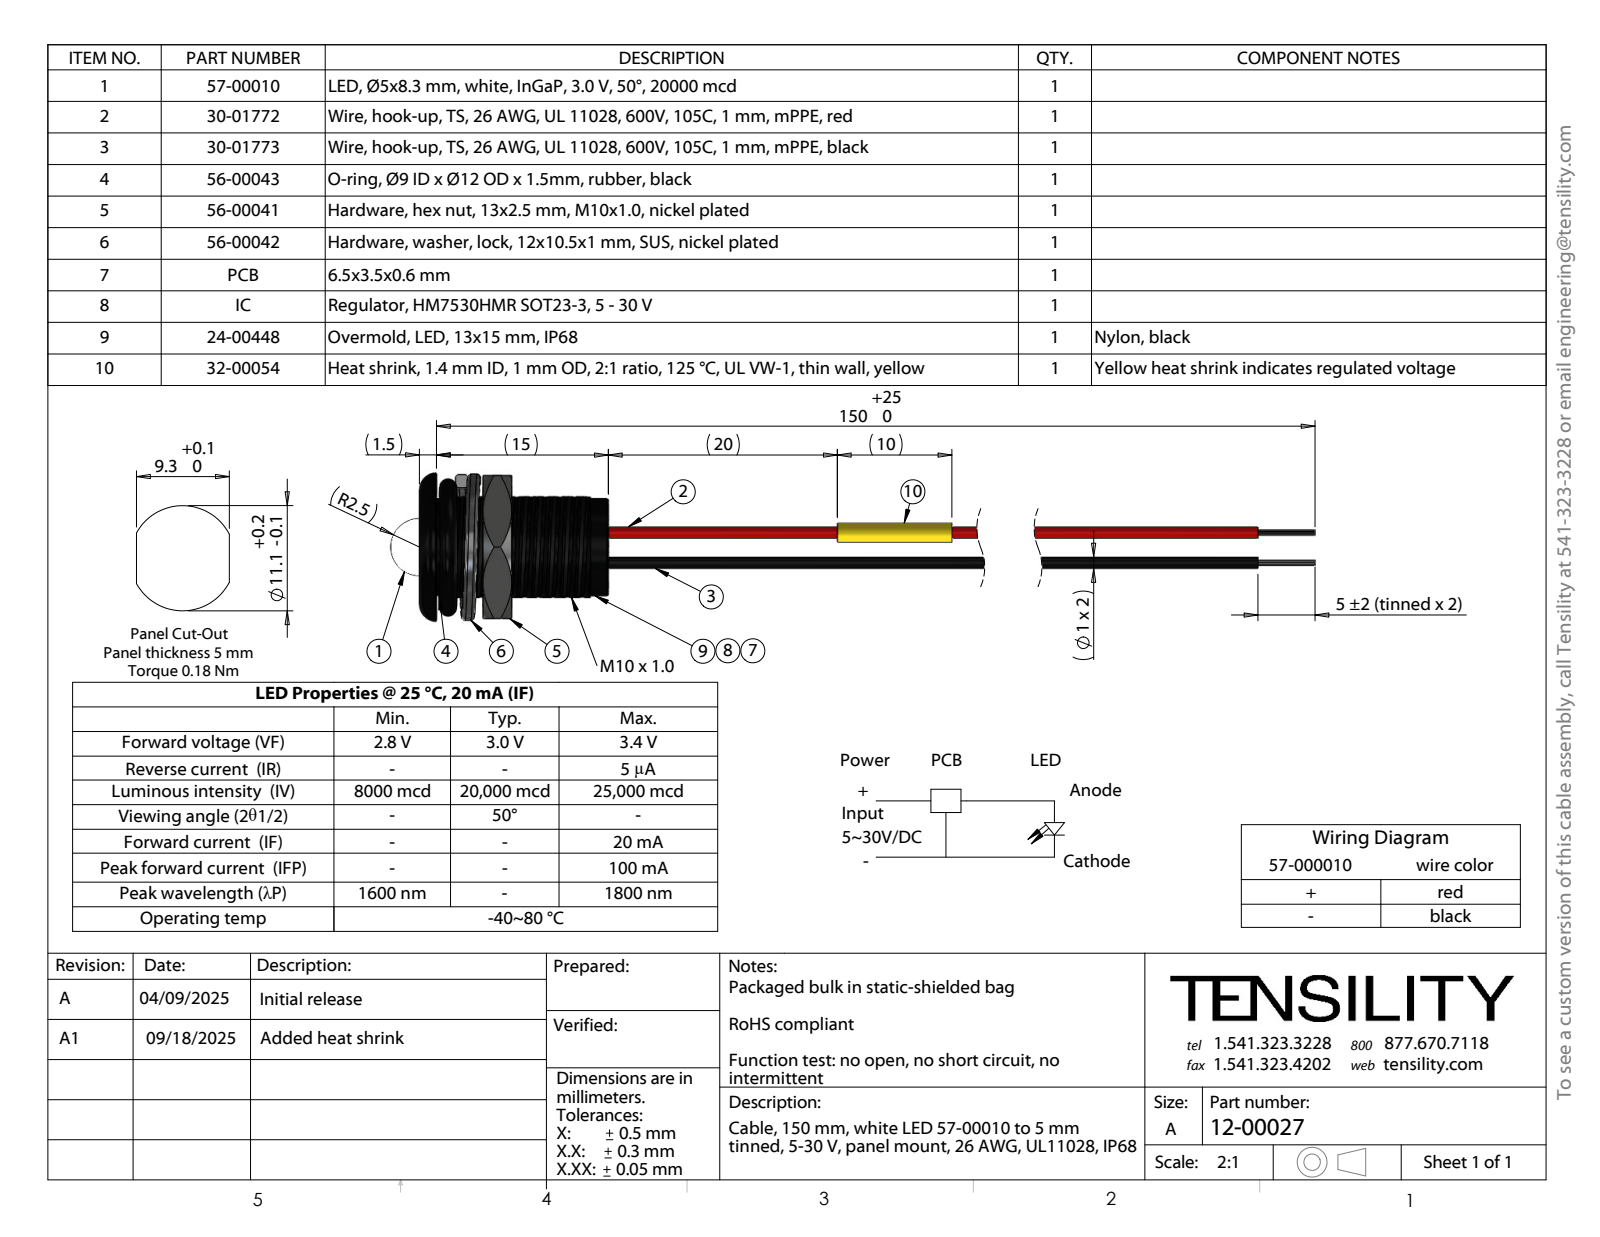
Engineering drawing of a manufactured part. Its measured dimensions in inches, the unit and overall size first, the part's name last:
Units: inches
Overall size (bounding box): 6.85 × 0.568 × 0.511
Round holes (diameter × count): ⌀0.039 ×2
Round bosses / shafts (diameter × count): ⌀0.039 ×2, ⌀0.033 ×2, ⌀0.335 ×1, ⌀0.197 ×1
Partial cylindrical surfaces — rounded edges, fillets, slot ends (radius × count): R0.17 ×1, R0.197 ×1
Main face-to-face distances: 0.059, 0.65, 0.591, 0.492, 0.317, 0.258, 0.332, 0.219, 0.16, 0.098
Hole centre spacings: 0.014, 0.015, 0.013, 0.096, 0.093, 0.098, 0.099, 0.101
Volume: 0.108 in³ · Surface area: 10.18 in²
Bodies: 57 solids, 514 faces (185 planar, 246 cylindrical, 83 other)
Part name (STEP PRODUCT): 30-01773_stripped and tinned; 56-00043; 57-00010_trimmed leads; 30-01772_stripped and tinned (+4 more)
STEP written by: SolidWorks 2021 (CONFIG_CONTROL_DESIGN)
